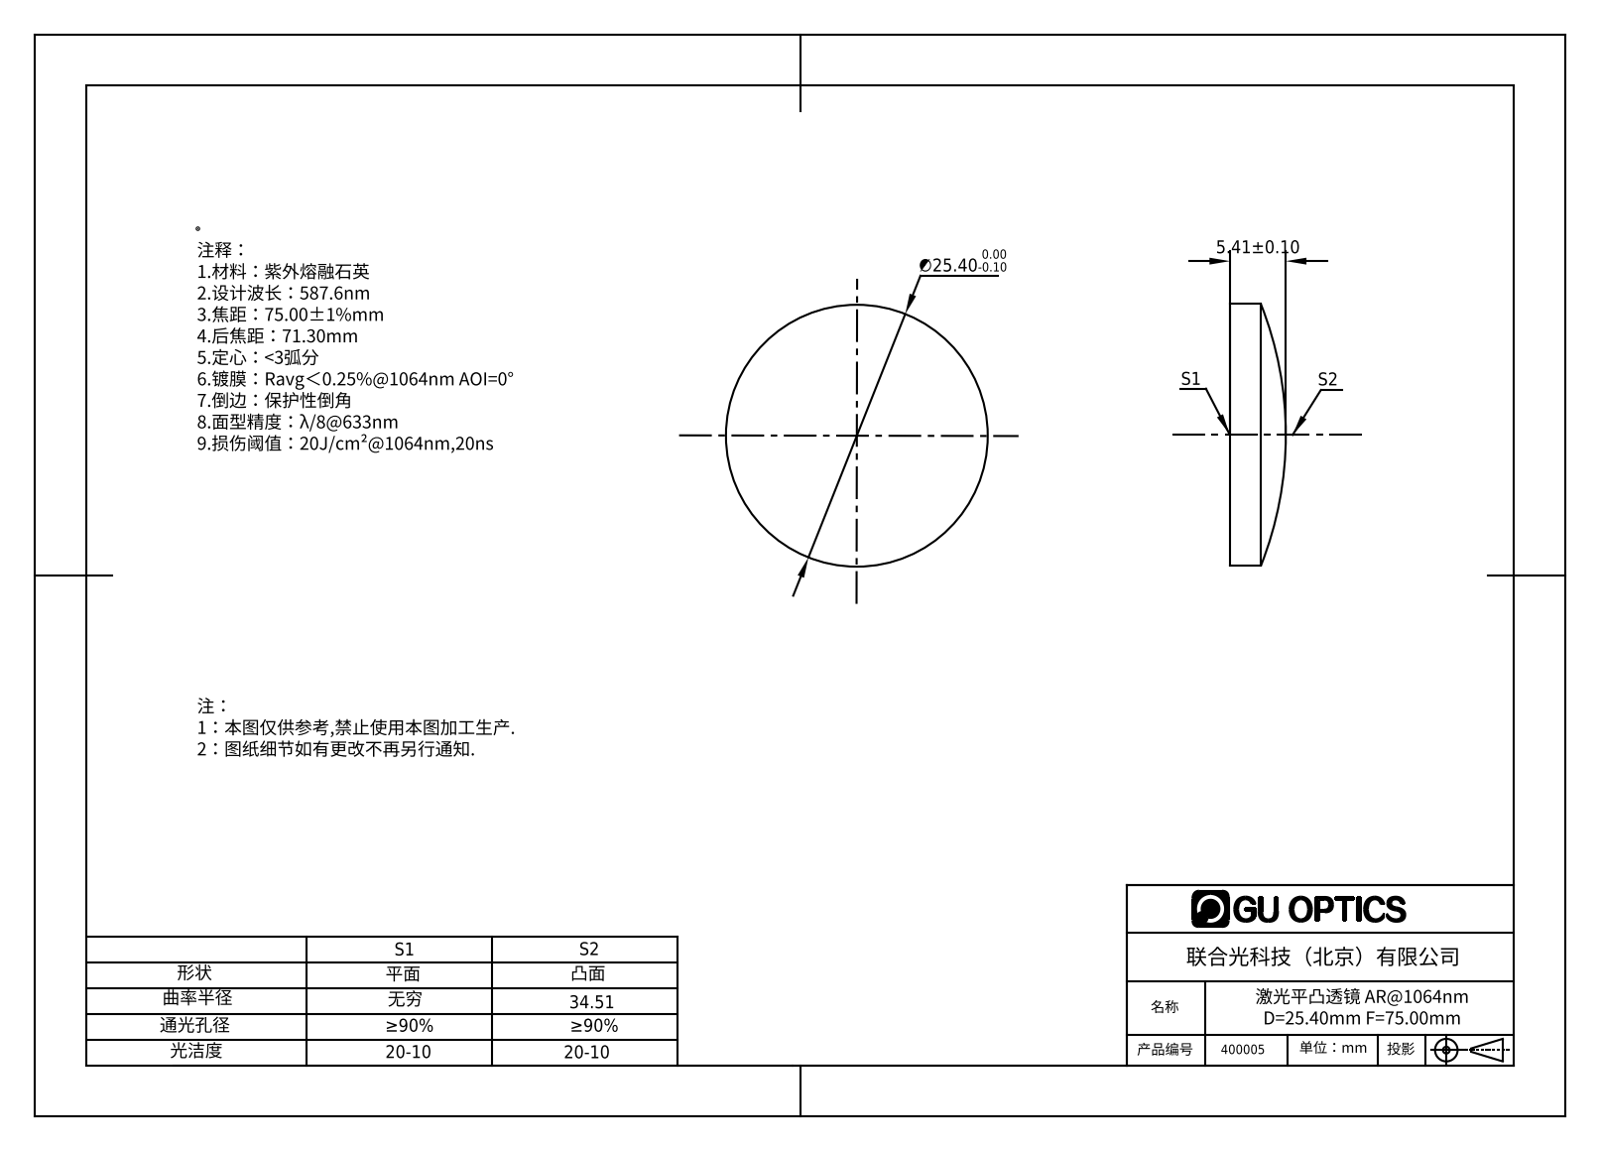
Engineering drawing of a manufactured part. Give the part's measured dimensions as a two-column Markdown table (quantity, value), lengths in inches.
| quantity | value |
| --- | --- |
| part name | 400005 |
| STEP written by | SolidWorks 2016 (AUTOMOTIVE_DESIGN) |
| units | inches |
| bodies | 1 solid, 5 faces (1 planar, 2 cylindrical, 2 other) |
| overall size | 1 × 1 × 0.213 |
| volume | 0.13 in³ |
| surface area | 1.969 in² |
| round bosses / shafts (diameter × count) | 1 × 1 |
